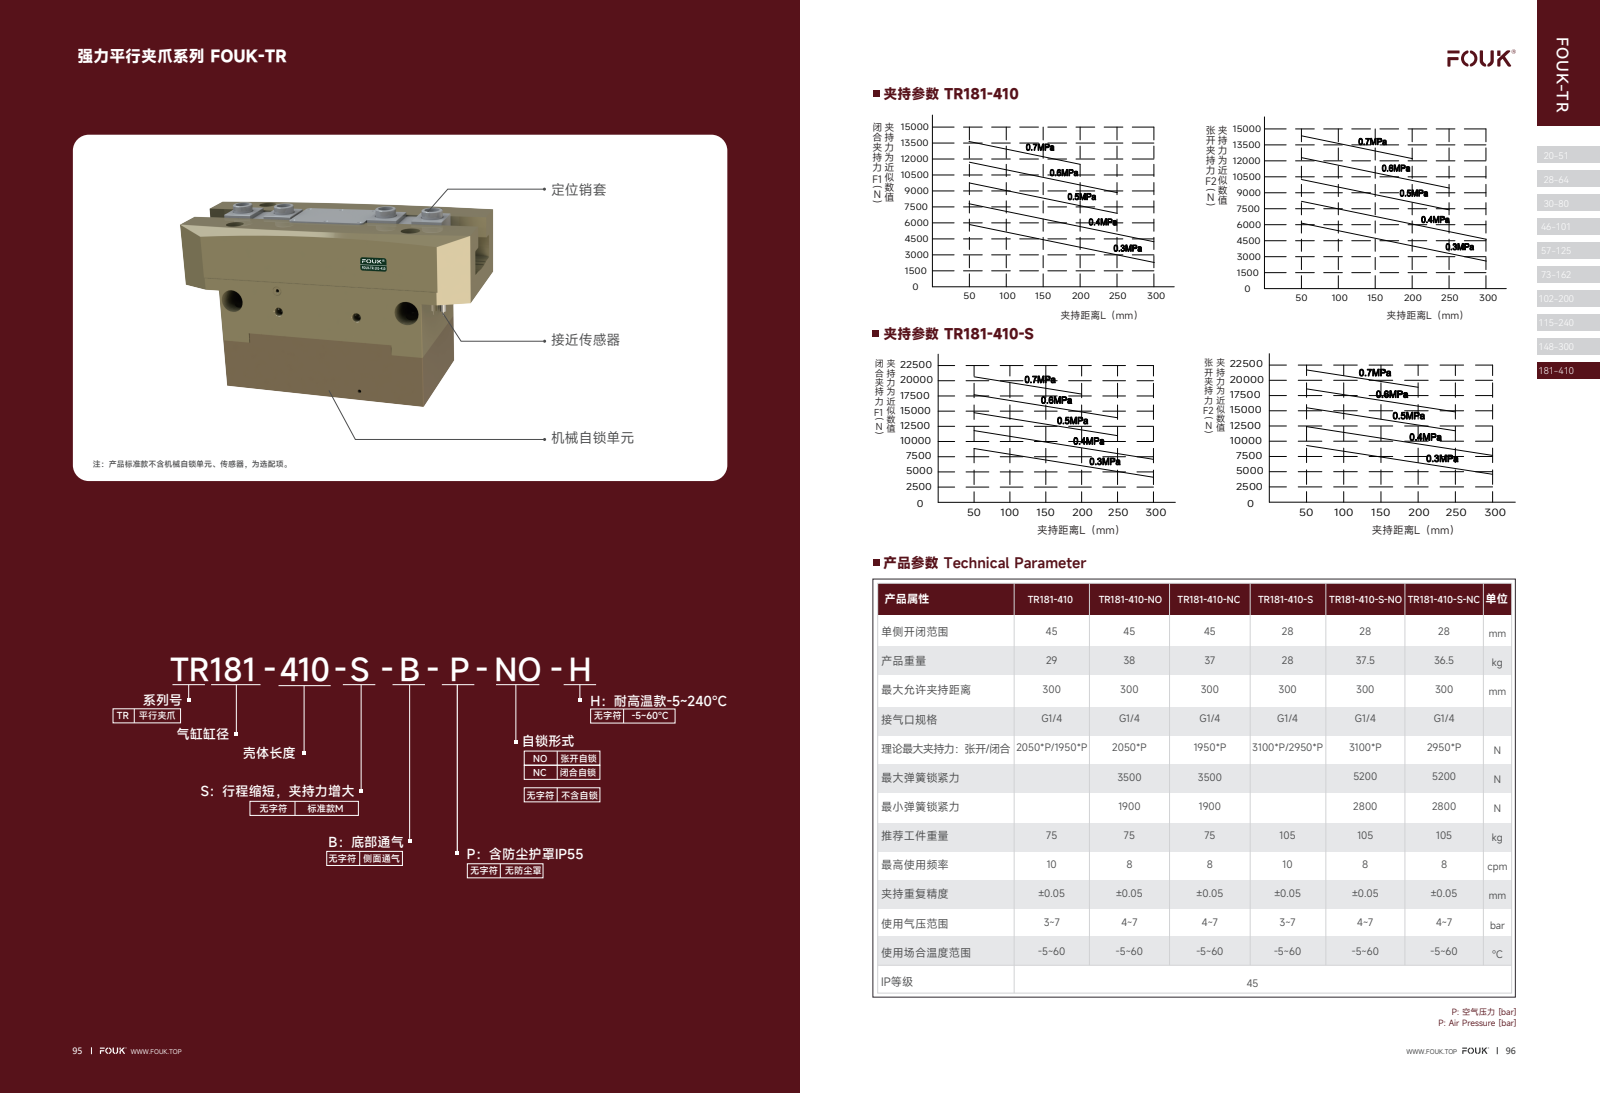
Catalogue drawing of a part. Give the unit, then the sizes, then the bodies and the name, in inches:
Units: inches
Overall size (bounding box): 16.142 × 6.969 × 6.772
Round holes (diameter × count): ⌀0.098 ×10, ⌀0.689 ×8, ⌀1.102 ×8, ⌀0.134 ×6, ⌀0.165 ×6, ⌀0.13 ×5, ⌀0.472 ×4, ⌀0.787 ×4, ⌀0.984 ×4, ⌀0.327 ×3, ⌀0.197 ×2, ⌀0.315 ×2
Round bosses / shafts (diameter × count): ⌀0.079 ×4, ⌀0.15 ×2, ⌀0.185 ×1, ⌀0.091 ×1
Partial cylindrical surfaces — rounded edges, fillets, slot ends (radius × count): R0.005 ×18, R0.005 ×12, R0.118 ×11, R0.02 ×4, R0.079 ×4, R0.217 ×4, R0.622 ×4, R0.63 ×4
Main face-to-face distances: 2.362, 3.504, 5.866, 0.02, 6.752, 1.102, 1.732, 5.039, 1.713, 5.02
Hole centre spacings: 2.52, 1.636, 1.89, 2.311, 2.344, 2.506, 2.507, 3.028
Volume: 549.3 in³ · Surface area: 1 059 in²
Bodies: 20 solids, 1269 faces (617 planar, 337 cylindrical, 315 other)
Part name (STEP PRODUCT): TR380-T-04 中位封板(默认); 20-28ПъМЧ-1; 20-28ПъМЧ; 20-28ПъМЧ-2 (+3 more)
STEP written by: SolidWorks 2018 (CONFIG_CONTROL_DESIGN)
